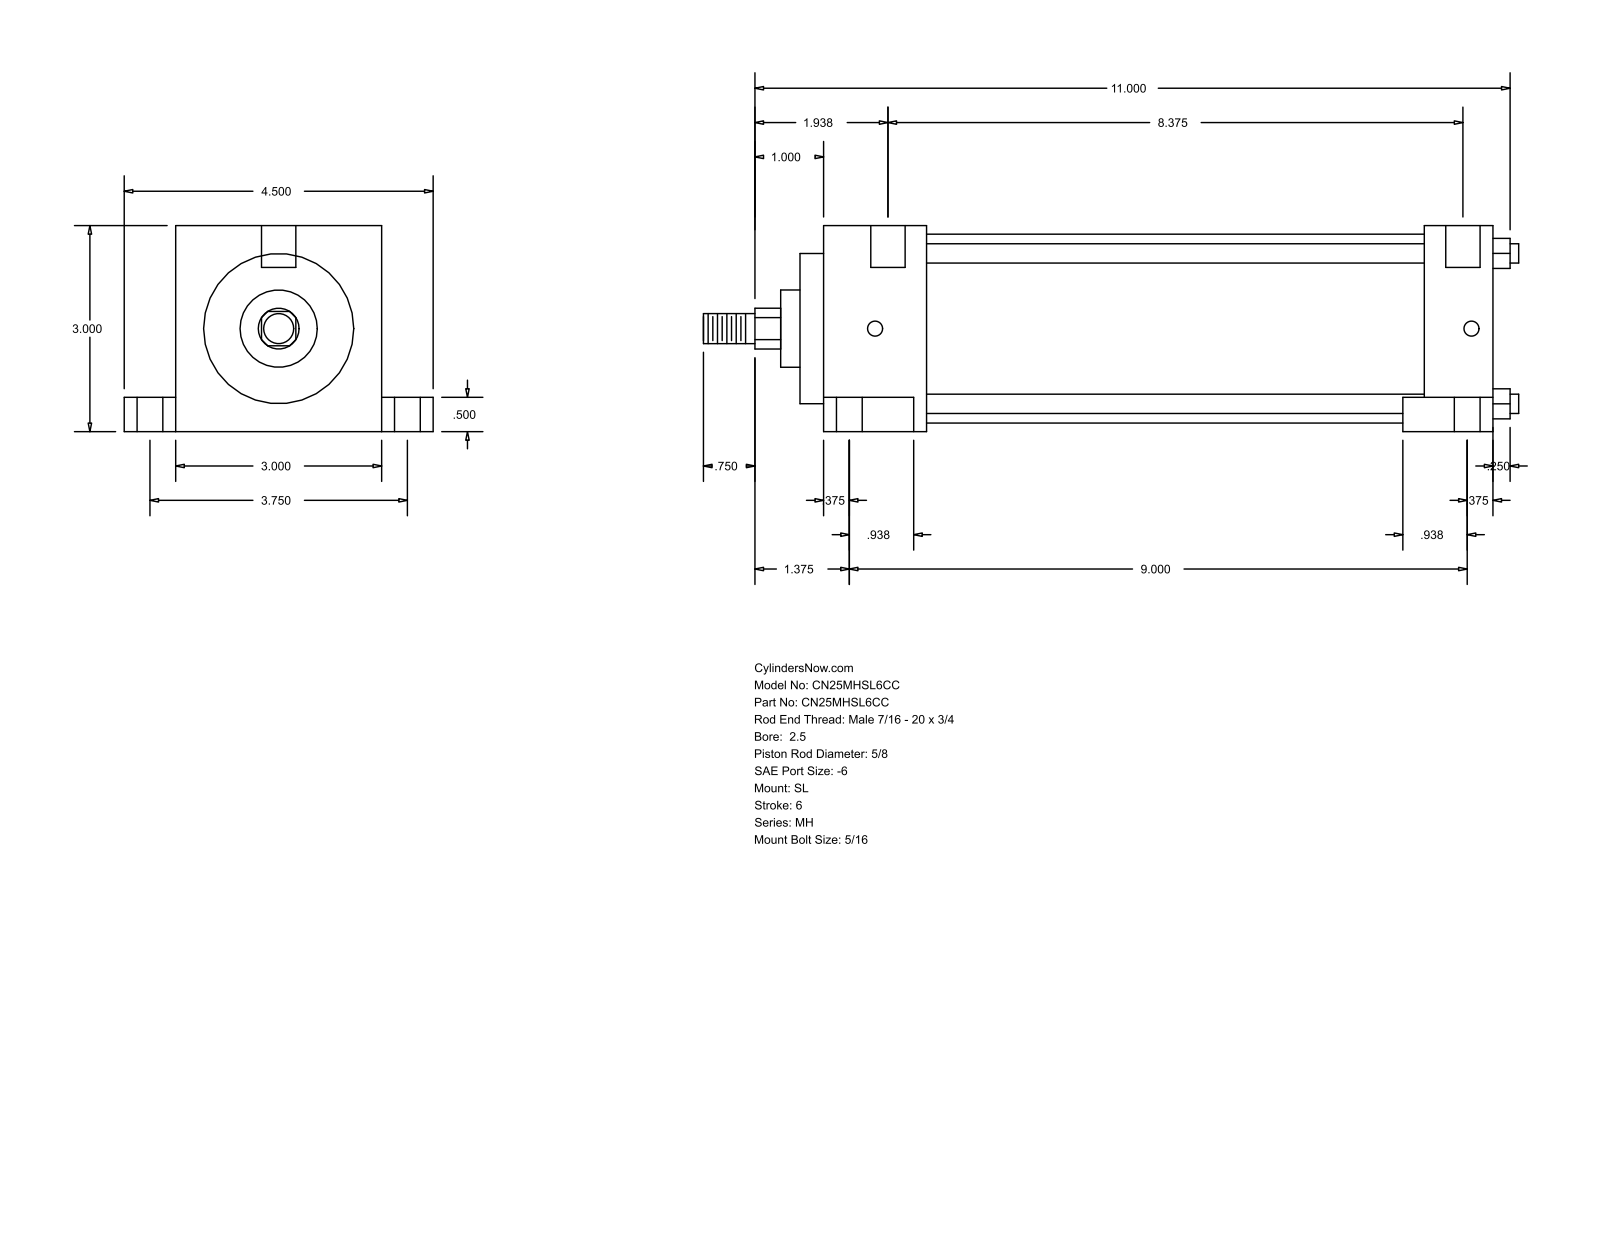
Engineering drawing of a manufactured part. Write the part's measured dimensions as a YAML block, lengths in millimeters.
part_name: "MH_SL__0250_0.625"
step_written_by: "GSSL Pune (CONFIG_CONTROL_DESIGN)"
units: millimeters
bodies: {solids: 0, faces: 86, planar: 61, cylindrical: 25, other: 0}
overall_size: [301.62, 114.3, 76.2]
round_holes:
  - {diameter: 5.56, count: 2}
  - {diameter: 9.53, count: 2}
  - {diameter: 15.88, count: 2}
  - {diameter: 12.7, count: 1}
round_bosses_or_shafts:
  - {diameter: 7.14, count: 4}
  - {diameter: 69.85, count: 1}
  - {diameter: 55.55, count: 1}
  - {diameter: 28.57, count: 1}
  - {diameter: 15.88, count: 1}
  - {diameter: 11.11, count: 1}
partial_cylinders:
  - {radius: 7.54, count: 1}
face_to_face_distances: [76.2, 25.4, 230.98, 256.38, 63.5, 12.7, 19.05, 95.25, 31.75, 223.04]
hole_center_spacings: [47.65, 3.17, 95.24]
